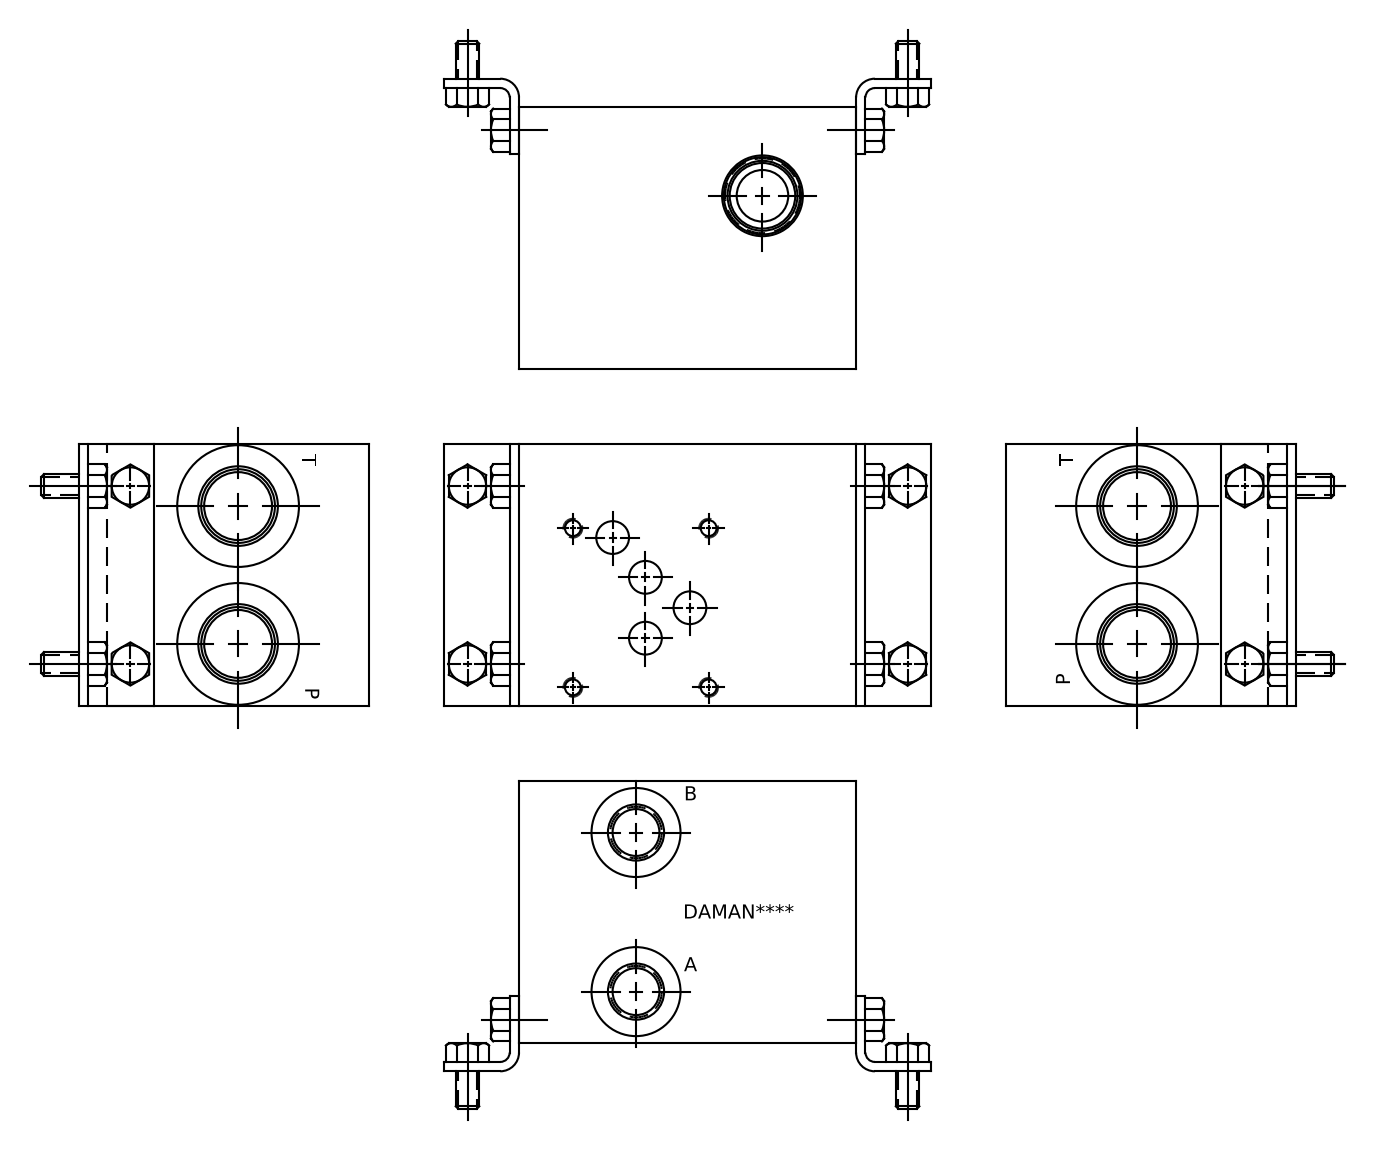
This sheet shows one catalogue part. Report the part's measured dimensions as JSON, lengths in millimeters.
{"part_name": "Part_AD05P013S~S.C01783R5_3D", "step_written_by": "Autodesk Inventor 2019 (AUTOMOTIVE_DESIGN)", "units": "millimeters", "bodies": {"solids": 1, "faces": 548, "planar": 312, "cylindrical": 55, "other": 181}, "overall_size": [114.3, 88.9, 88.9], "volume_mm3": 791869, "surface_area_mm2": 76236, "round_holes": [[5.11, 4], [6.35, 4], [6.53, 2], [7.92, 2], [11.11, 2], [11.13, 2], [15.88, 2], [17.5, 2], [19.05, 2], [19.25, 2], [21.18, 2], [24.92, 2]], "face_to_face_distances": [88.9, 114.3, 0.79, 113.51, 112.72, 88.11, 19.05, 19.84, 94.46, 93.67], "hole_center_spacings": [29.74, 37.16, 46.05, 64.82, 70.95, 13.88, 17.49, 18.28]}
